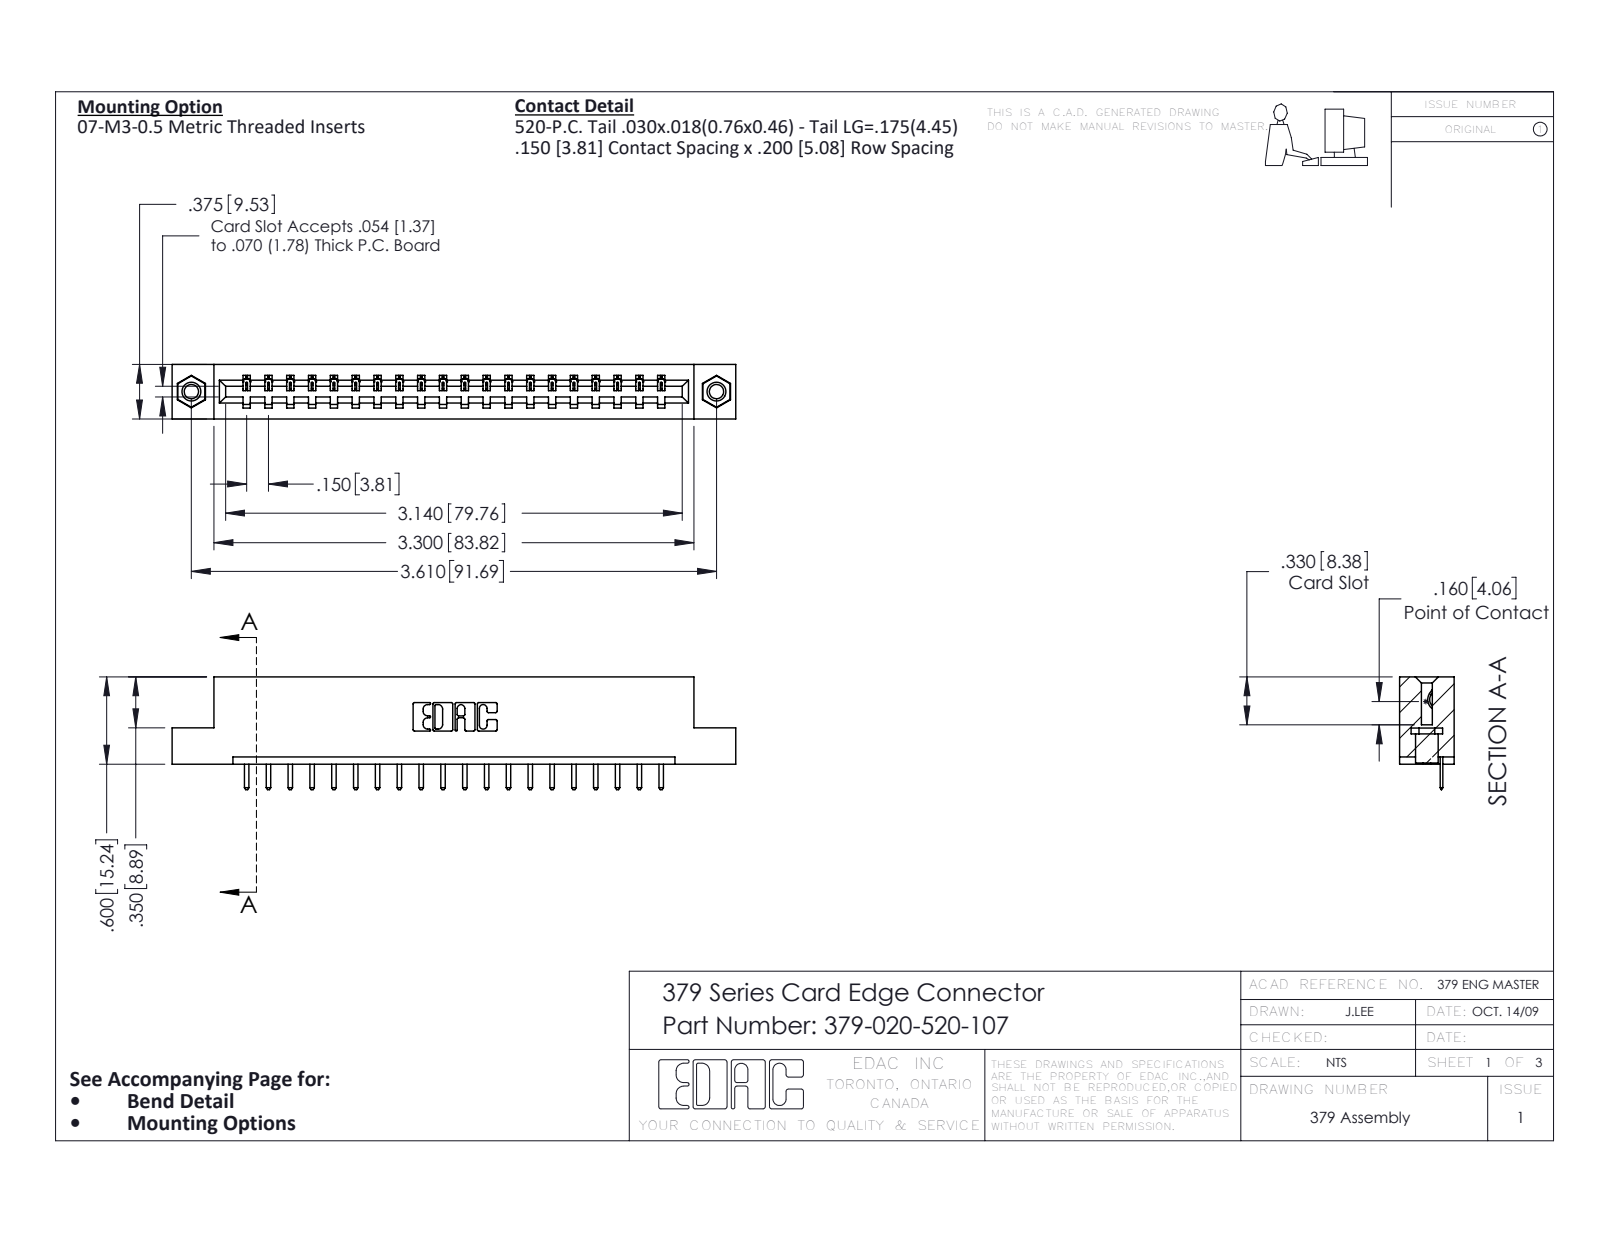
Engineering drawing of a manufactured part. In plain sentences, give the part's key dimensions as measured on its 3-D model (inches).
The part is named "379-020-520-107; 345-250-001_345-250-005-103; 345-292-001_345-293-120; 379 Part_Flush - .156 Dia - TI". Its 3-D file was written by "SolidWorks 2016 (CONFIG_CONTROL_DESIGN)". It is 23 solids with 1414 faces: 982 planar, 416 cylindrical and 16 other. Overall it measures 3.875 by 0.775 by 0.375 inches. Its volume is 0.611 cubic inches and its surface area 15.44 square inches. Round holes: 2 of diameter 0.098, 2 of diameter 0.125, 2 of diameter 0.156. Round bosses or shafts: 2 of diameter 0.155. Partial cylindrical surfaces (rounded edges, fillets, slot ends): 42 of radius 0.01, 40 of radius 0.006, 22 of radius 0.01, 6 of radius 0.007, 6 of radius 0.031, 3 of radius 0.026, 1 of radius 0.014, 1 of radius 0.022. The main face-to-face distances are 0.3, 0.375, 0.075, 0.6, 0.225, 0.15, 0.45, 0.75, 0.55, 0.2. The hole center spacings are 3.61.
